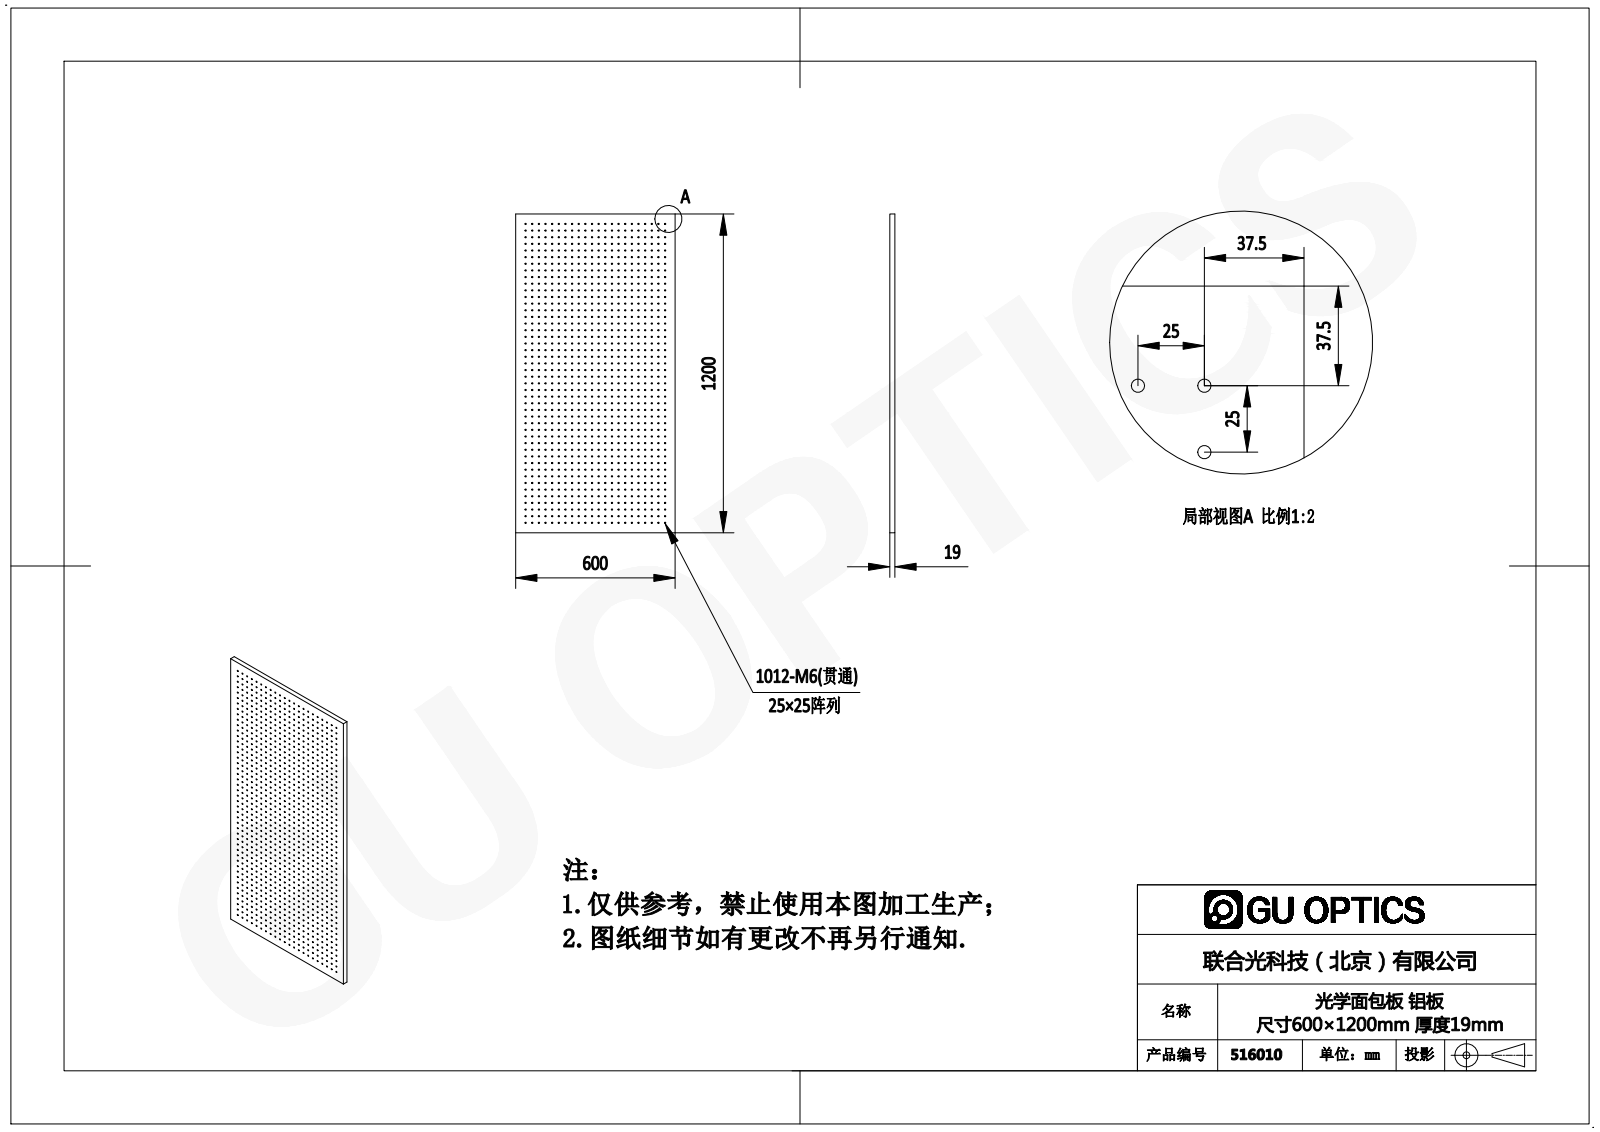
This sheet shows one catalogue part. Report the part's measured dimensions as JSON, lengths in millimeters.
{"part_name": "516010", "step_written_by": "SolidWorks 2016 (AUTOMOTIVE_DESIGN)", "units": "millimeters", "bodies": {"solids": 1, "faces": 2030, "planar": 6, "cylindrical": 2024, "other": 0}, "overall_size": [1200, 600, 19], "volume_mm3": 13300000, "surface_area_mm2": 1771000, "round_holes": [[5, 1012]], "face_to_face_distances": [19, 600, 1200], "hole_center_spacings": [25, 50, 75, 100, 125, 150, 175, 200]}
